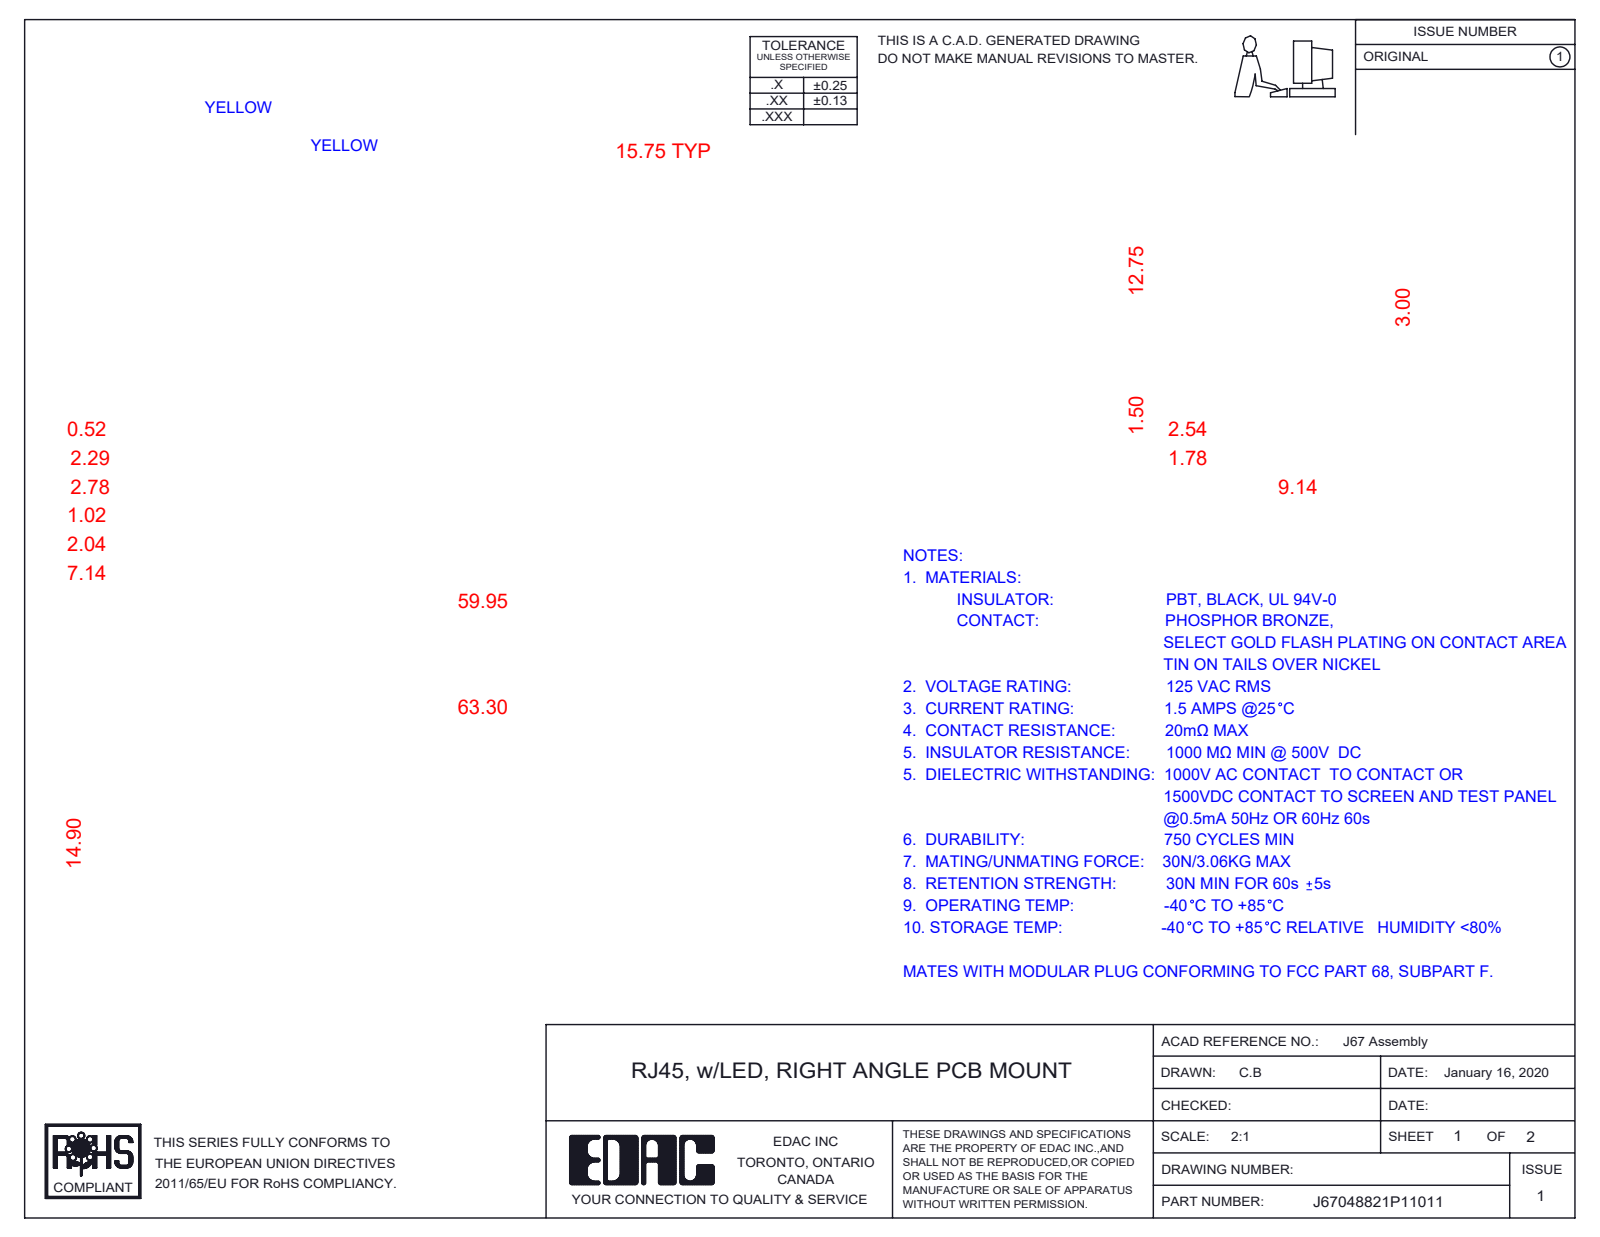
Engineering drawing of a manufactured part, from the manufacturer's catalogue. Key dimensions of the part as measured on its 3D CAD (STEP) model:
Part name (STEP PRODUCT): 67 Insulator; 67 LED LH_1-Yellow; 67 Contacts; 67 LED RH_1-Yellow (+1 more)
STEP written by: SolidWorks 2016 (CONFIG_CONTROL_DESIGN)
Units: millimetres
Bodies: 41 solids, 2465 faces (1781 planar, 476 cylindrical, 208 other)
Overall size (bounding box): 63.3 × 16.25 × 15.28
Volume: 5 159 mm³ · Surface area: 11 573 mm²
Round bosses / shafts (diameter × count): ⌀0.46 ×96
Partial cylindrical surfaces — rounded edges, fillets, slot ends (radius × count): R0.2 ×66, R0.3 ×29, R0.45 ×9, R1.55 ×8, R1.5 ×2, R1.7 ×2, R0.35 ×1, R1 ×1
Main face-to-face distances: 0.5, 12.55, 1.89, 0.89, 10, 15.75, 1, 1.39, 11, 11.89
